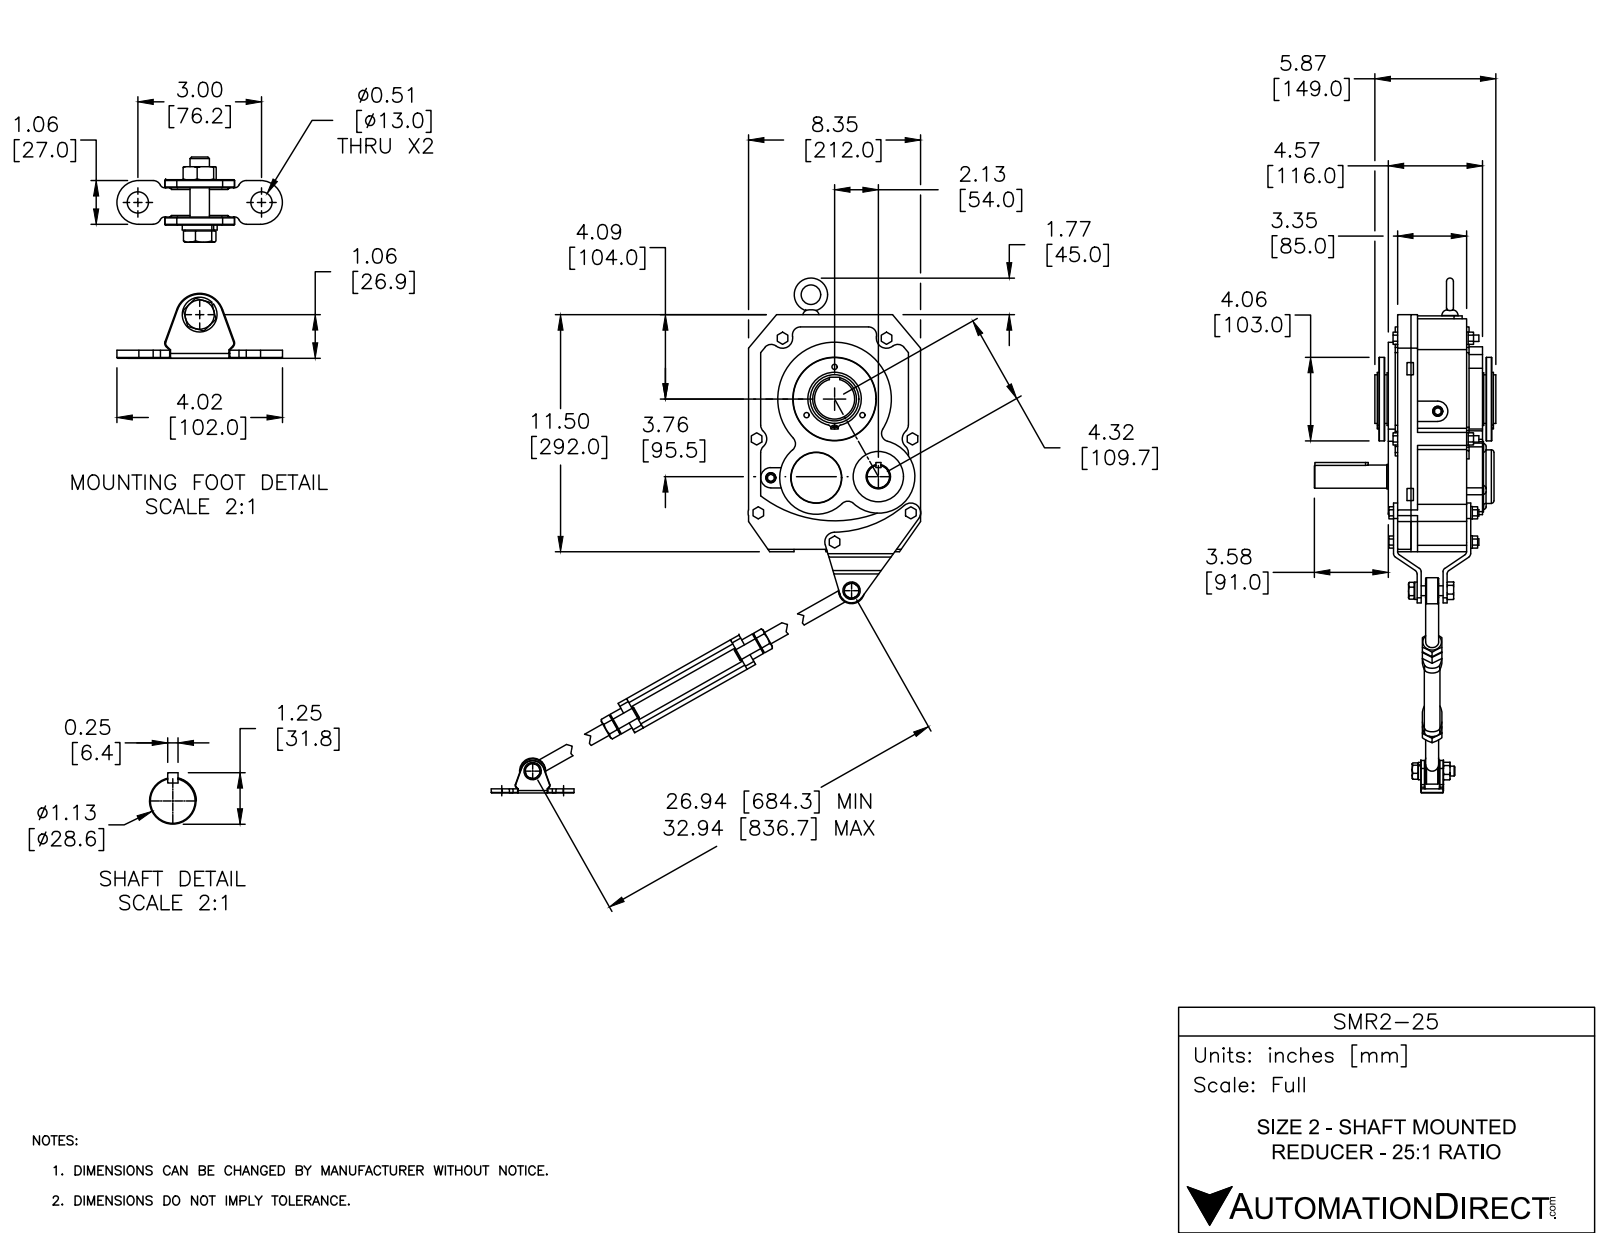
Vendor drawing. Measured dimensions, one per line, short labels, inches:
name: SMR2-TA_3; SMR2-TA_2; SMR2-TA_1; SMR2-25_REDUCER (+4 more)
written by: SolidWorks 2016 (AUTOMOTIVE_DESIGN)
unit: in
bodies: 58 solids, 1229 faces (599 planar, 435 cylindrical, 195 other)
size: 32.574 × 31.591 × 8.799
volume: 364 in³; area: 1 056 in²
holes: 8× ⌀0.313, 7× ⌀0.315, 7× ⌀0.374, 3× ⌀0.256, 3× ⌀0.472, 3× ⌀0.484, 3× ⌀0.512, 2× ⌀0.098, 2× ⌀0.48, 2× ⌀0.508, 2× ⌀0.63, 1× ⌀0.551
bosses: 7× ⌀0.606, 4× ⌀0.413, 3× ⌀0.472, 2× ⌀1.26, 2× ⌀0.878, 2× ⌀0.846, 2× ⌀0.709, 2× ⌀0.63
rounds: 22× R0.02, 19× R0.394, 16× R0.197, 8× R0.118, 8× R0.492, 4× R0.079, 3× R0.236, 2× R0.039
face distances: 3.465, 0.65, 0.768, 0.453, 0.197, 1.102, 0.118, 4.567, 3.799, 3.346
hole spacings: 2.5, 3.535, 1.563, 2.707, 1.07, 1.336, 1.378, 1.38
